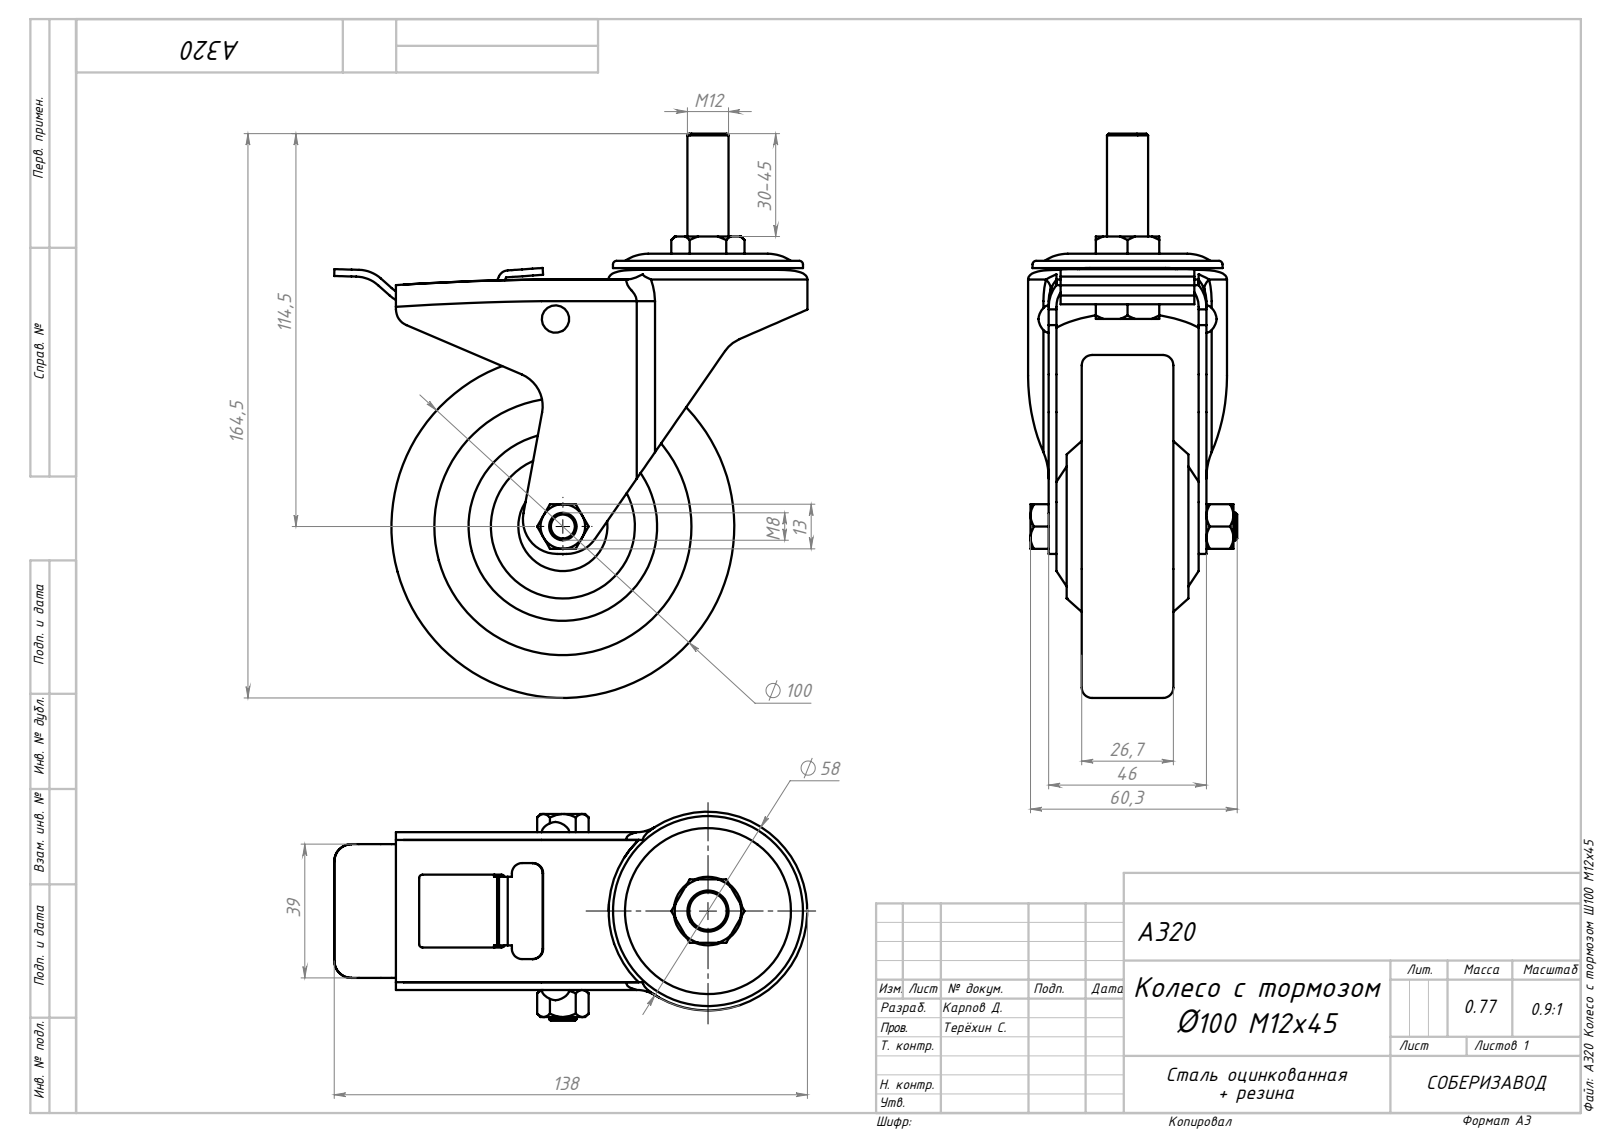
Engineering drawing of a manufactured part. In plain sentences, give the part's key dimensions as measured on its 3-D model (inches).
The part is named "Болт_00; A320 Гайка_00; Основание_00; Крышка_00 (+6 more)". Its 3-D file was written by "SolidWorks 2021 (AUTOMOTIVE_DESIGN)". It is 11 solids with 404 faces: 186 planar, 78 cylindrical and 140 other. Overall it measures 6.478 by 5.433 by 2.402 inches. Its volume is 11.58 cubic inches and its surface area 136.7 square inches. Round holes: 1 of diameter 0.268, 1 of diameter 0.315, 1 of diameter 0.472, 1 of diameter 1.811, 1 of diameter 2.559. Round bosses or shafts: 1 of diameter 3.937, 1 of diameter 2.181, 1 of diameter 1.969. Partial cylindrical surfaces (rounded edges, fillets, slot ends): 12 of radius 0.394, 5 of radius 0.118, 4 of radius 0.039, 3 of radius 0.197, 2 of radius 0.079, 1 of radius 1.053, 1 of radius 1.142, 1 of radius 31.66. The main face-to-face distances are 0.089, 1.722, 0.38, 1.431, 0.291, 1.343, 0.512, 0.892, 0.919, 0.803.
